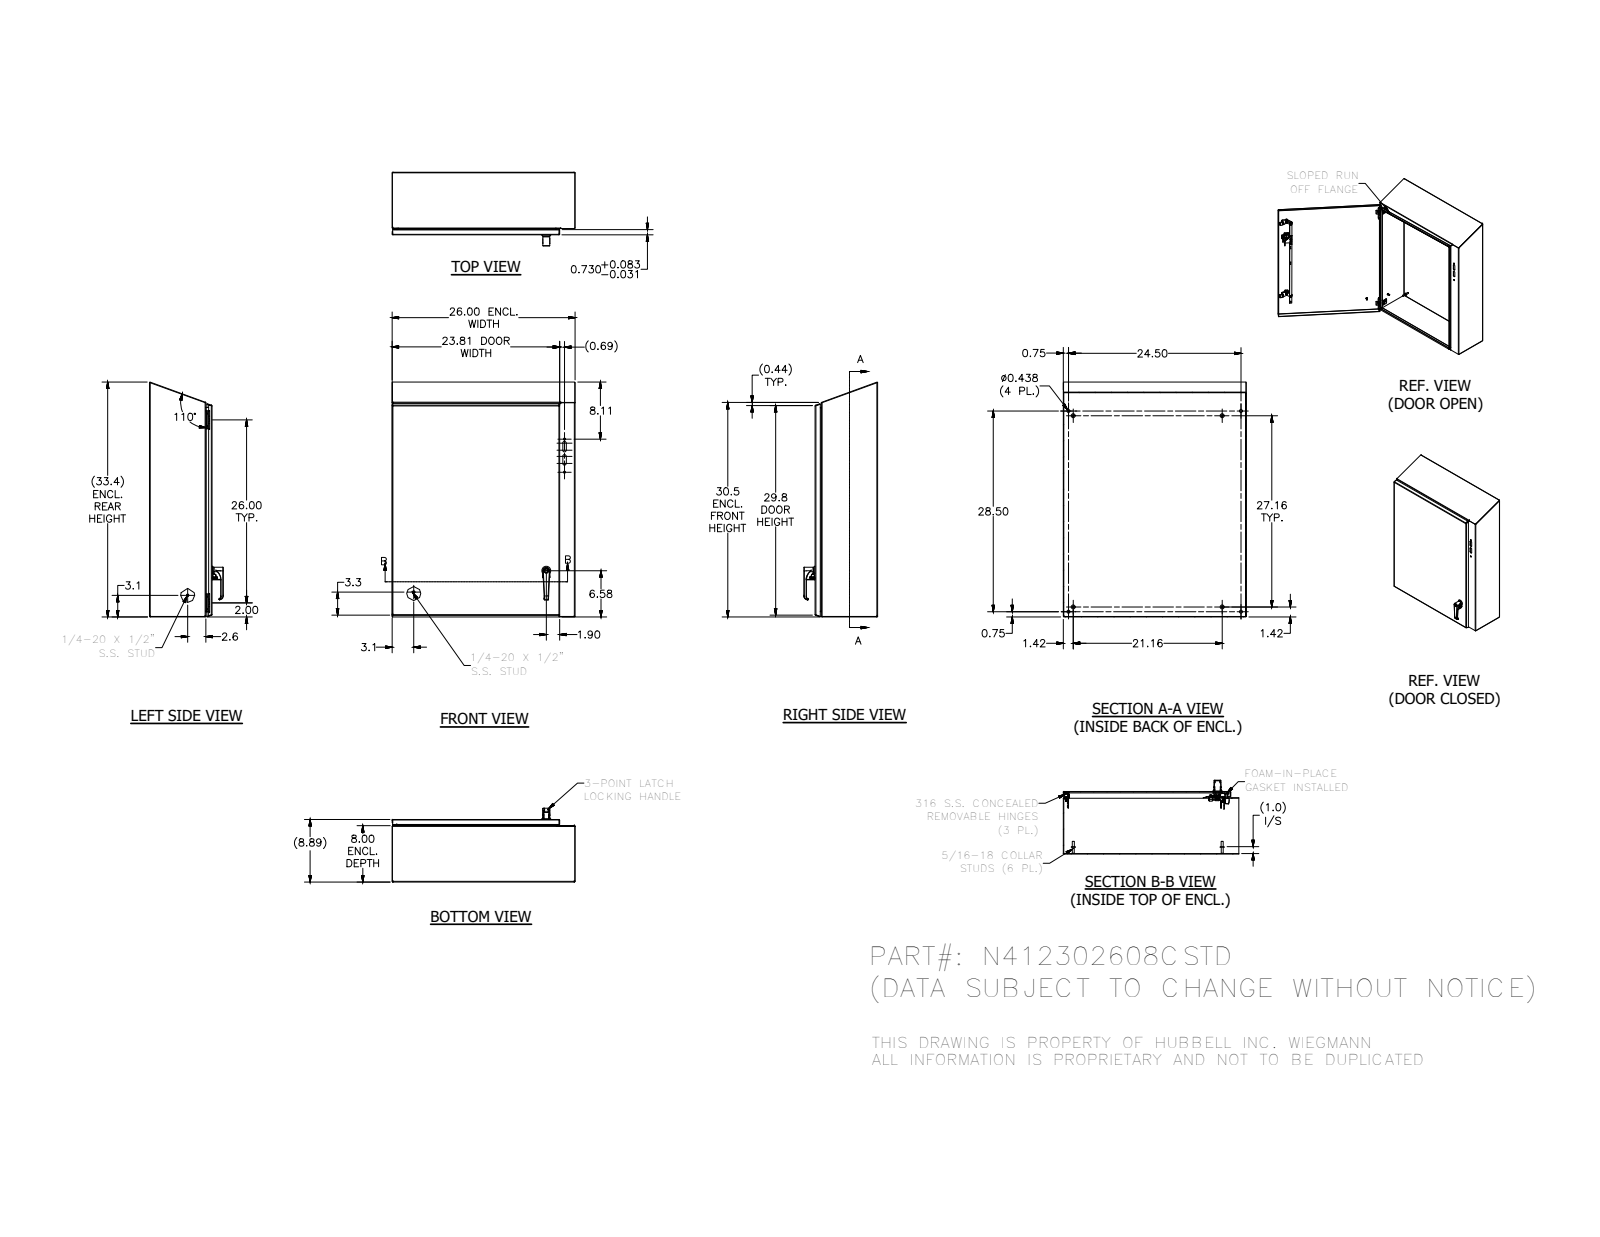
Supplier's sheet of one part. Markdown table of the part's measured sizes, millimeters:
| quantity | value |
| --- | --- |
| part name | N412302608CSTDB3S; 388150; N4122608CSTDTOP; 38846 (+8 more) |
| STEP written by | Autodesk Inventor 2014 (AUTOMOTIVE_DESIGN) |
| units | millimeters |
| bodies | 62 solids, 2137 faces (861 planar, 753 cylindrical, 523 other) |
| overall size | 847.49 × 660.4 × 266.22 |
| volume | 3 515 000 mm³ |
| surface area | 3 711 000 mm² |
| round holes (diameter × count) | 3.68 × 6, 3.96 × 5, 2.36 × 4, 3.86 × 4, 4.25 × 4, 4.37 × 4, 4.76 × 4, 11.11 × 4, 8.13 × 3, 4.98 × 2, 5.36 × 2, 5.59 × 2 |
| round bosses / shafts (diameter × count) | 6.35 × 12, 7.62 × 8, 14.3 × 4, 11.11 × 4, 9.14 × 4, 8.13 × 4, 6.99 × 4, 6.5 × 4 |
| partial cylindrical surfaces (radius × count) | 0.5 × 38, 0.3 × 30, 0.79 × 29, 1.27 × 26, 3.17 × 25, 2.67 × 19, 0.4 × 18, 0.64 × 16 |
| main face-to-face distances | 1.88, 223.84, 221.96, 225.72, 658.52, 201.32, 22.52, 660.4, 656.64, 20.64 |
| hole center spacings | 660.4, 12.7, 523.88, 523.87, 632.46, 16.66, 16.76, 25 |
